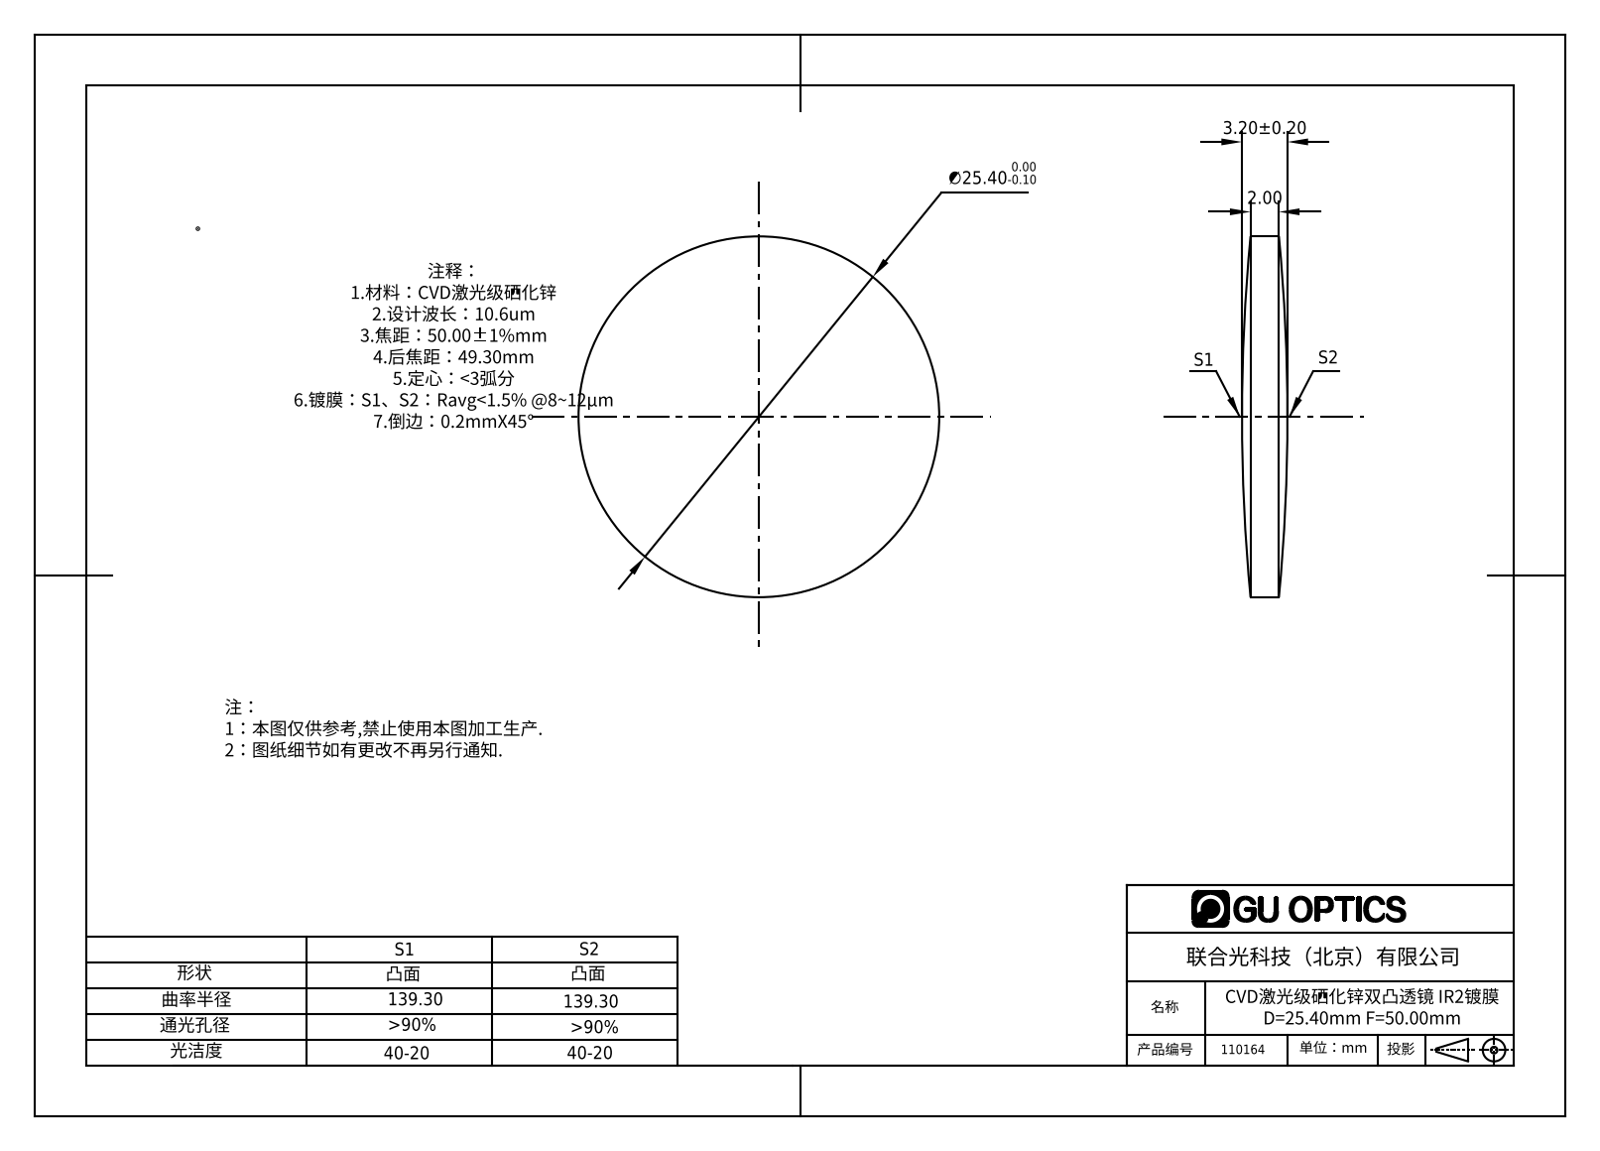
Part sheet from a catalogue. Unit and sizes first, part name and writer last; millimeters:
Units: millimetres
Overall size (bounding box): 25.4 × 25.4 × 3.2
Round bosses / shafts (diameter × count): ⌀25.4 ×1
Volume: 1 317 mm³ · Surface area: 1 175 mm²
Bodies: 1 solid, 6 faces (0 planar, 2 cylindrical, 4 other)
Part name (STEP PRODUCT): 110156
STEP written by: SolidWorks 2016 (CONFIG_CONTROL_DESIGN)
